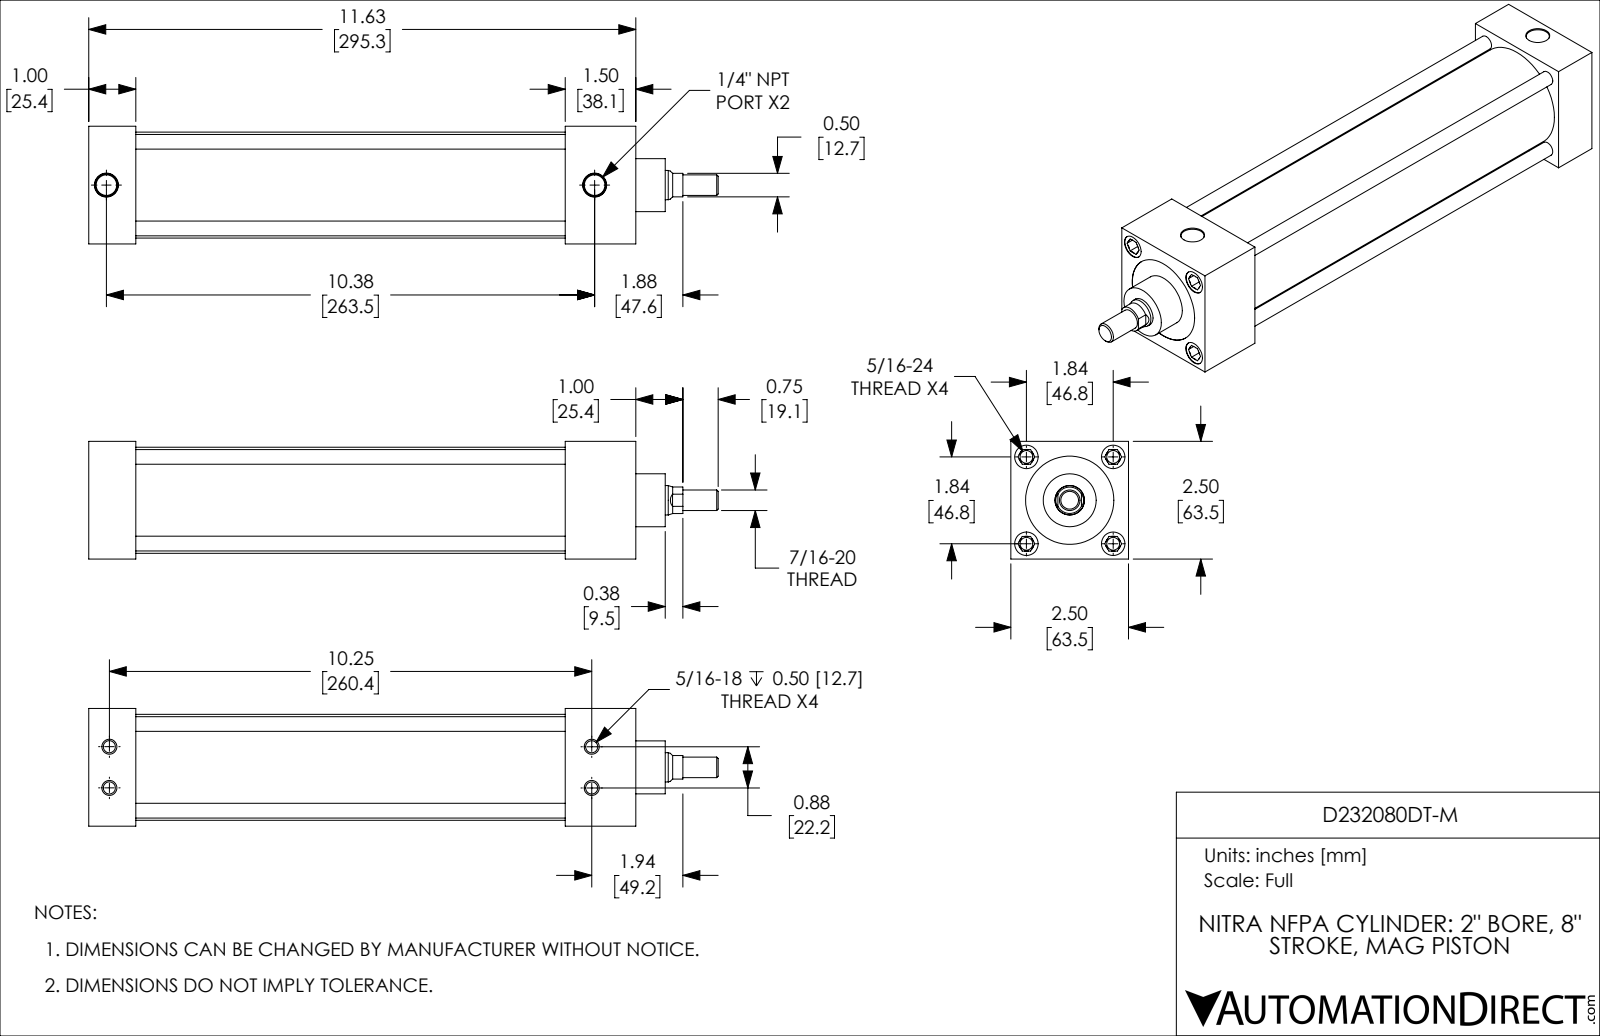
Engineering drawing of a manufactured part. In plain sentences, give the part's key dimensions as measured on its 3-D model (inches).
The part is named "D232080DT-M; D232080DT-M_PISTON_KK1; D232080DT-M_BODY". Its 3-D file was written by "SolidWorks 2019 (CONFIG_CONTROL_DESIGN)". It is 2 solids with 200 faces: 58 planar, 62 cylindrical and 80 other. Overall it measures 13.375 by 2.5 by 2.5 inches. Its volume is 32.03 cubic inches and its surface area 255.8 square inches. Round holes: 7 of diameter 0.272, 4 of diameter 0.257, 4 of diameter 0.5, 2 of diameter 0.438, 1 of diameter 0.626, 1 of diameter 1.875, 1 of diameter 2.001. Round bosses or shafts: 4 of diameter 0.312, 1 of diameter 2.251, 1 of diameter 1.999, 1 of diameter 1.125, 1 of diameter 0.624, 1 of diameter 0.437. Partial cylindrical surfaces (rounded edges, fillets, slot ends): 1 of radius 0.281. The main face-to-face distances are 2.5, 1, 10.125, 9.125, 2.125, 1.125, 8, 11.625, 10.625, 9.5. The hole center spacings are 1.84, 1.844, 1.301, 0.441, 0.443, 0.875, 1.304, 2.602.
